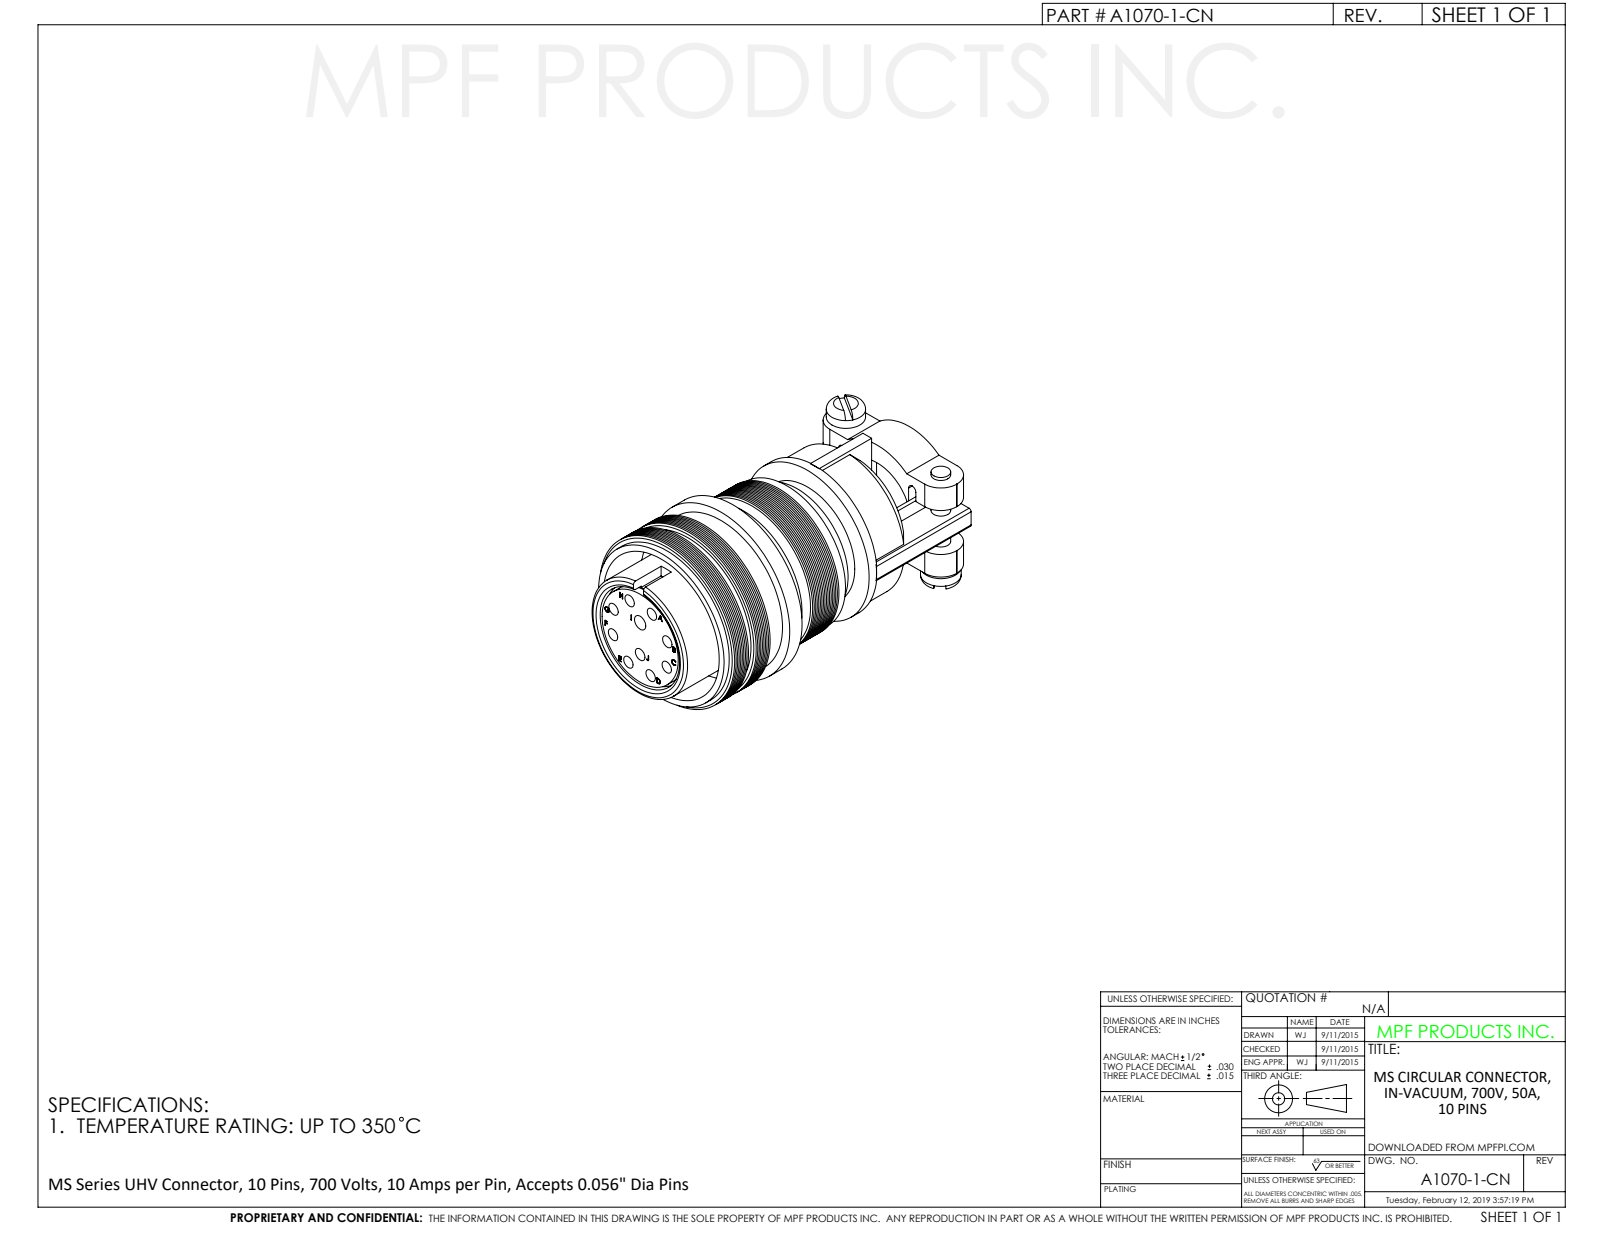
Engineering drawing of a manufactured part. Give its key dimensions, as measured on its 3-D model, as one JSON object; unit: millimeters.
{"part_name": "A1070-1-CN", "step_written_by": "SolidWorks 2012 (CONFIG_CONTROL_DESIGN)", "units": "millimeters", "bodies": {"solids": 1, "faces": 394, "planar": 113, "cylindrical": 99, "other": 182}, "overall_size": [69.5, 34, 34], "volume_mm3": 37130, "surface_area_mm2": 16500, "round_holes": [[2.2, 8], [1.9, 2], [14, 1], [19.8, 1], [28.6, 1]], "round_bosses_or_shafts": [[3.4, 2], [34, 1], [31.1, 1], [31, 1], [30.5, 1], [29, 1], [25.1, 1], [23.4, 1]], "partial_cylinders_radius": [[0.9, 8], [0.5, 4], [4, 4], [8.2, 1], [12, 1], [12, 1]], "face_to_face_distances": [30.3, 2.5, 16.3, 11.9, 18.3, 43.5, 5.1, 13.3, 25.2, 66.5], "hole_center_spacings": [5, 5, 6.5, 6.5, 9.2, 9.2, 9.6, 12]}
